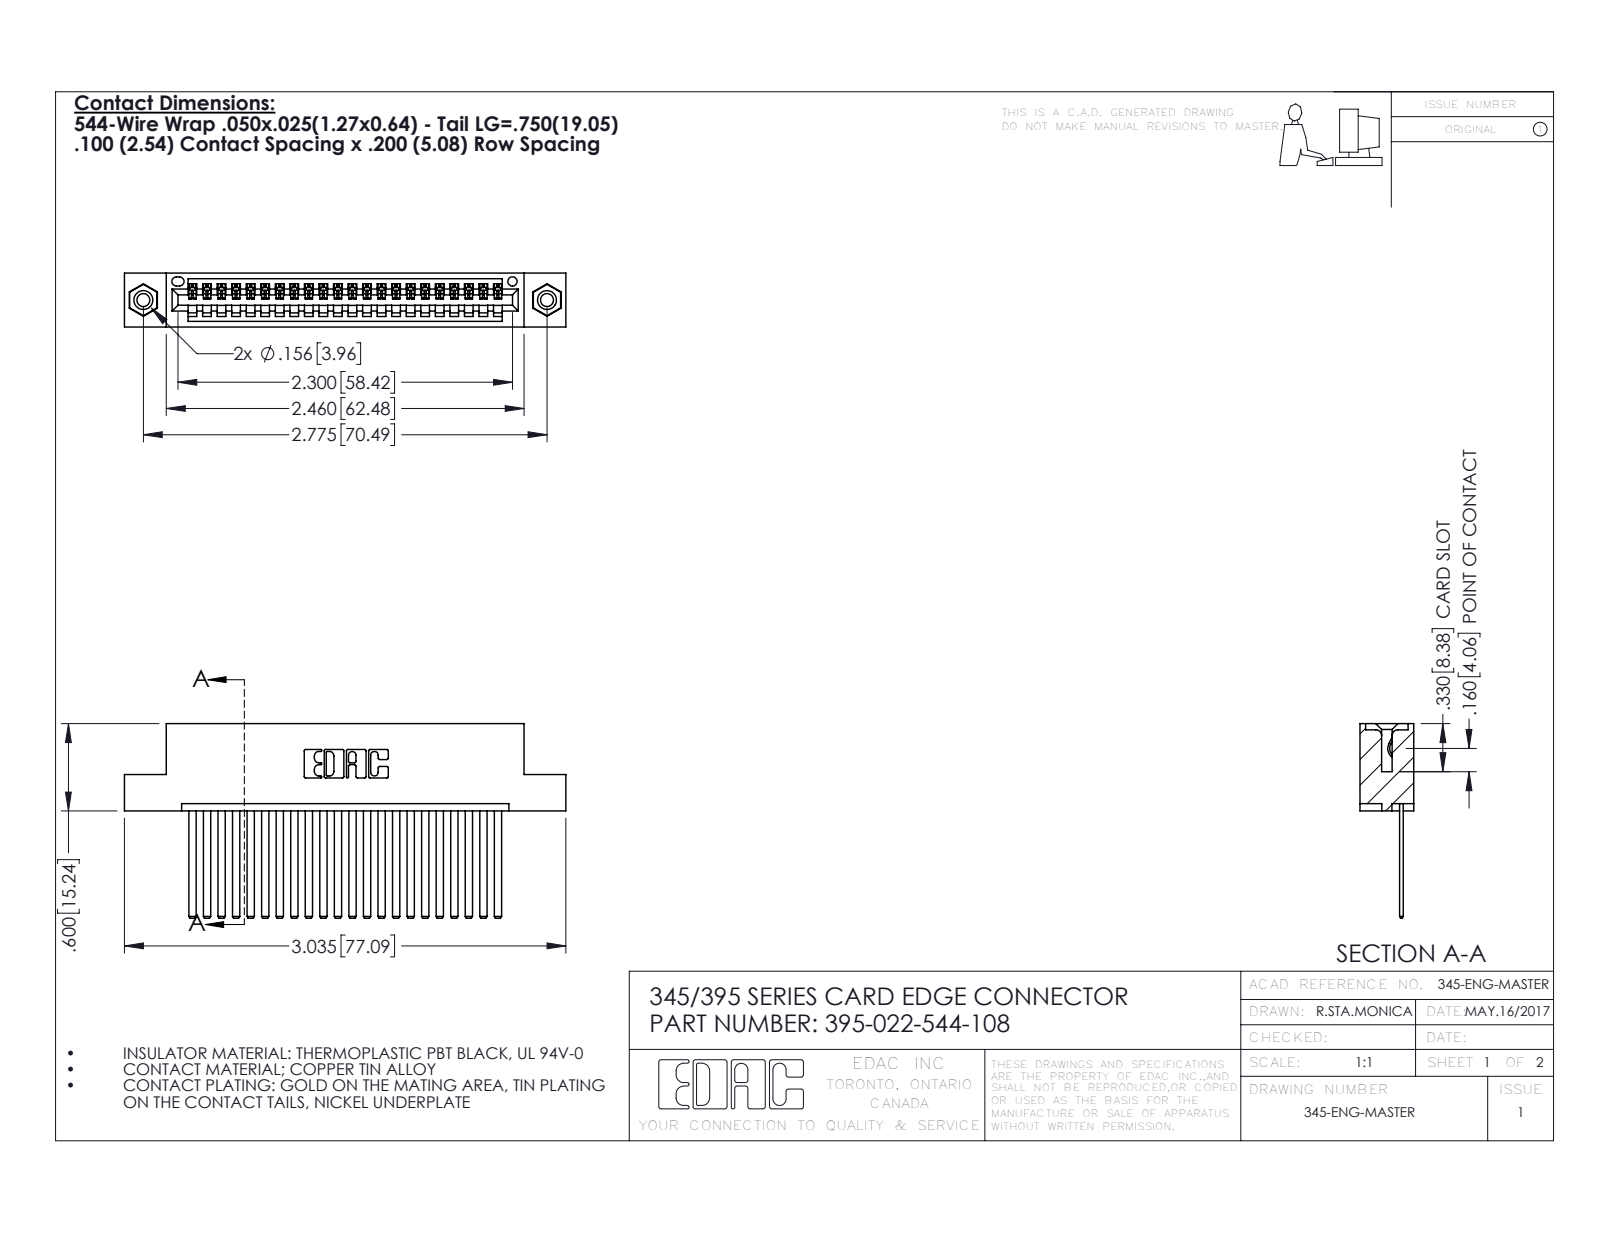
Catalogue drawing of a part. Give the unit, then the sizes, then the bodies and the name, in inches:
Units: inches
Overall size (bounding box): 3.035 × 1.337 × 0.37
Round holes (diameter × count): ⌀0.089 ×2, ⌀0.125 ×2, ⌀0.156 ×2, ⌀0.064 ×1
Round bosses / shafts (diameter × count): ⌀0.155 ×2
Partial cylindrical surfaces — rounded edges, fillets, slot ends (radius × count): R0.006 ×44, R0.01 ×22, R0.007 ×6, R0.031 ×6, R0.026 ×3, R0.031 ×2, R0.04 ×2, R0.014 ×1
Main face-to-face distances: 0.072, 0.298, 0.098, 0.272, 0.025, 0.2, 0.37, 0.225, 0.149, 0.072
Hole centre spacings: 0.27, 2.541, 2.775
Volume: 0.452 in³ · Surface area: 16.05 in²
Bodies: 25 solids, 1330 faces (904 planar, 410 cylindrical, 16 other)
Part name (STEP PRODUCT): 345-250-001_345-250-003-102; 395-022-544-108; 345 Part_Flush Mounting Lugs - 0.156 Dia-TI; 345-292-001_345-293-144
STEP written by: SolidWorks 2016 (CONFIG_CONTROL_DESIGN)
